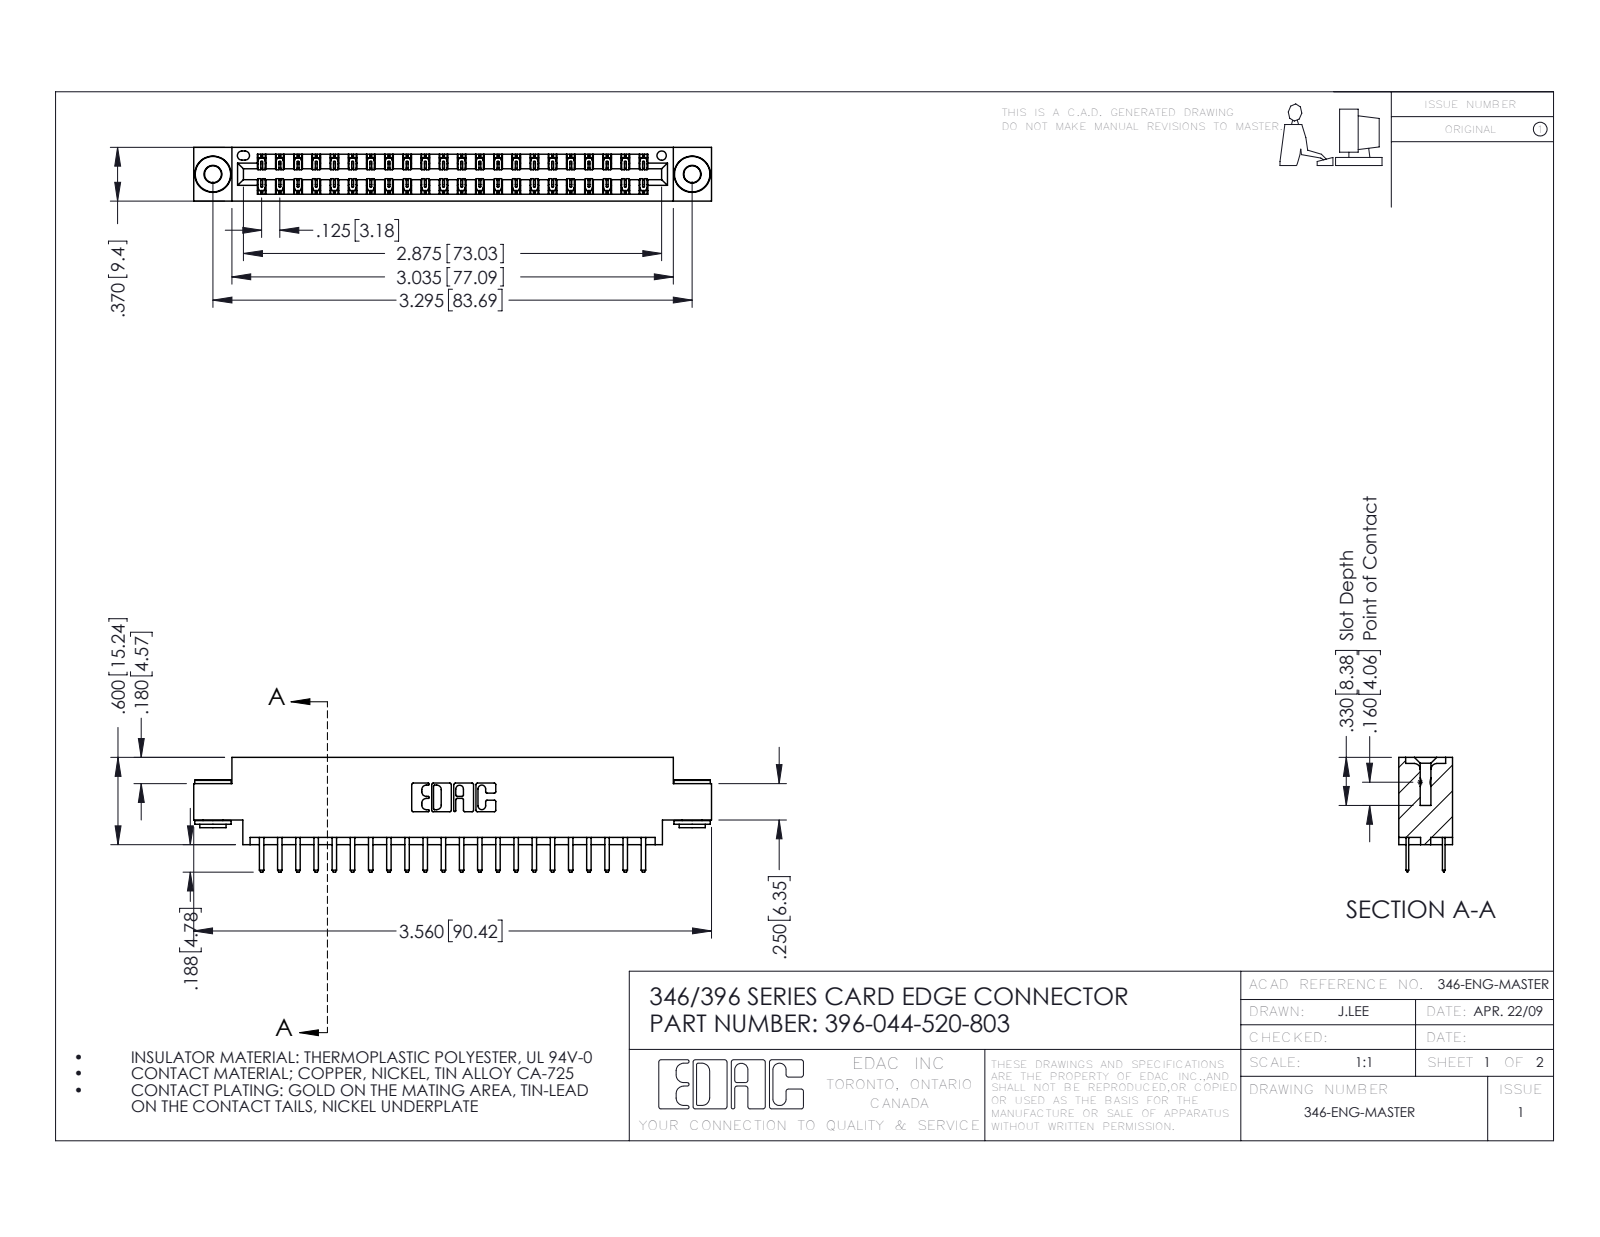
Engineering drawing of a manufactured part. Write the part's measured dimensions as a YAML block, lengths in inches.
part_name: "346 Part_0.170 Offset - 0.156 Dia-TH; 396-044-520-803; 345-250-002_345-250-002-102; 345-292-001_345-293-120"
step_written_by: "SolidWorks 2016 (CONFIG_CONTROL_DESIGN)"
units: inches
bodies: {solids: 47, faces: 2628, planar: 1718, cylindrical: 902, other: 8}
overall_size: [3.56, 0.788, 0.37]
volume: 0.519
surface_area: 18.18
round_holes:
  - {diameter: 0.116, count: 2}
  - {diameter: 0.156, count: 2}
  - {diameter: 0.064, count: 1}
round_bosses_or_shafts:
  - {diameter: 0.25, count: 2}
  - {diameter: 0.18, count: 2}
  - {diameter: 0.136, count: 2}
partial_cylinders:
  - {radius: 0.006, count: 66}
  - {radius: 0.01, count: 48}
  - {radius: 0.01, count: 22}
  - {radius: 0.007, count: 6}
  - {radius: 0.031, count: 6}
  - {radius: 0.026, count: 3}
  - {radius: 0.014, count: 2}
  - {radius: 0.022, count: 2}
face_to_face_distances: [0.048, 0.322, 0.37, 0.25, 0.025, 0.275, 0.072, 0.298, 0.148, 0.222]
hole_center_spacings: [0.246, 3.087, 3.295]
